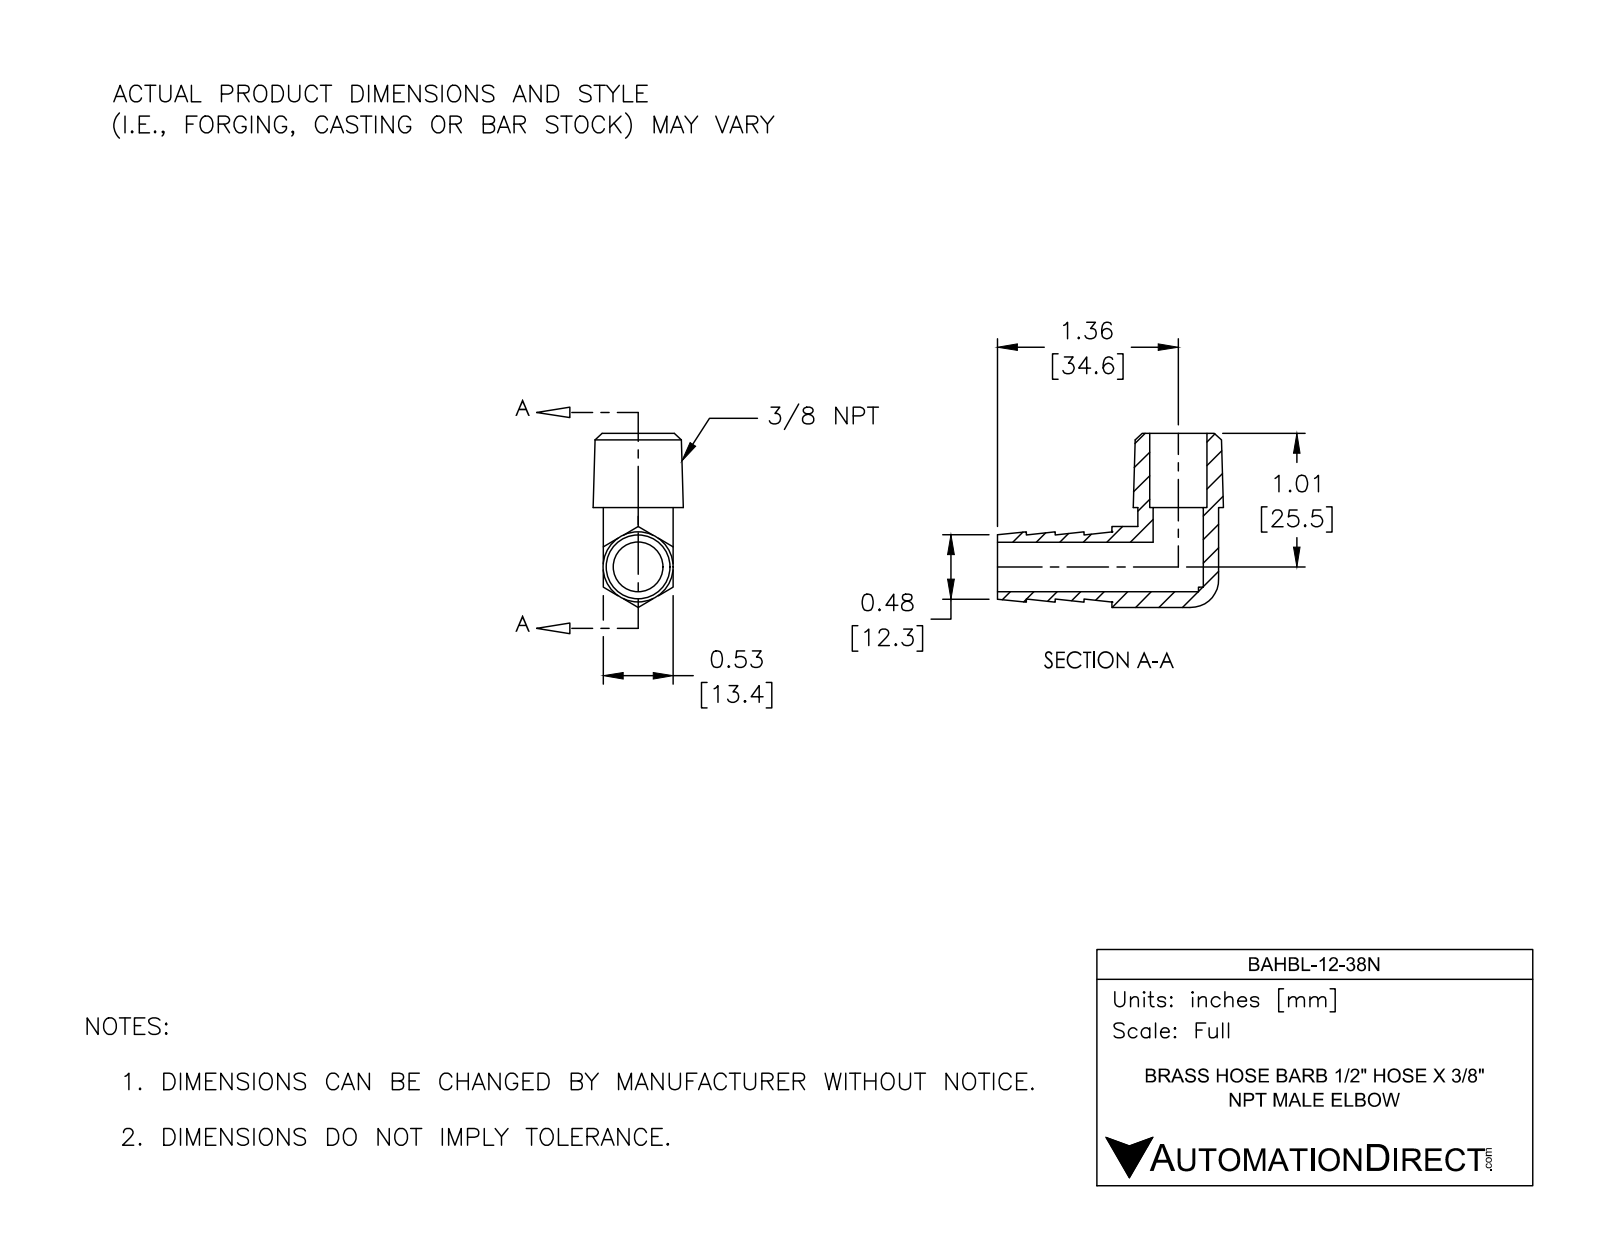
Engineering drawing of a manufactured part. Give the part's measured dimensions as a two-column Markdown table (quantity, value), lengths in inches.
| quantity | value |
| --- | --- |
| part name | BAHBL-12-38N |
| STEP written by | SolidWorks 2017 (AUTOMOTIVE_DESIGN) |
| units | inches |
| bodies | 1 solid, 57 faces (27 planar, 18 cylindrical, 12 other) |
| overall size | 1.7 × 1.31 × 0.679 |
| volume | 0.303 in³ |
| surface area | 7.638 in² |
| round holes (diameter × count) | 0.373 × 1, 0.378 × 1, 0.43 × 1, 0.529 × 1 |
| partial cylindrical surfaces (radius × count) | 0.25 × 2 |
| main face-to-face distances | 0.527, 0.527, 0.217, 0.558, 0.434, 0.6, 1.158, 0.651, 0.862, 1.079 |
